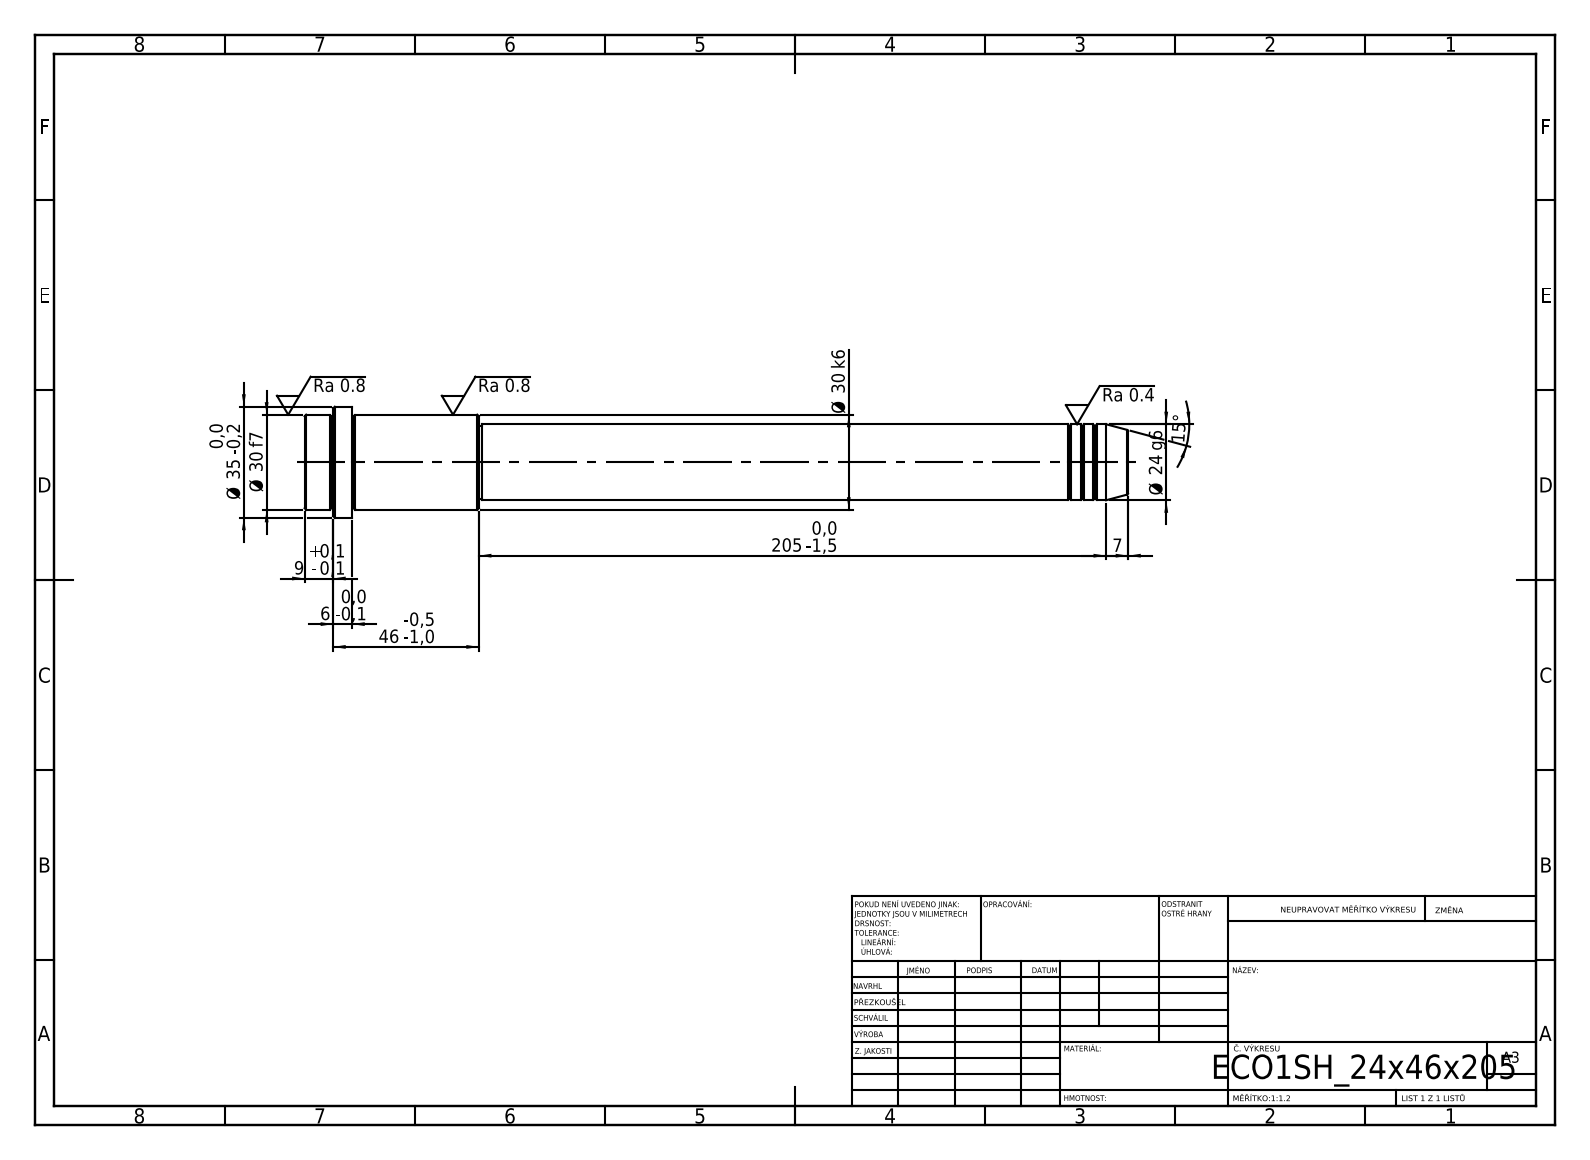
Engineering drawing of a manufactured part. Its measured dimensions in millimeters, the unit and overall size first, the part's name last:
Units: millimetres
Overall size (bounding box): 260 × 35 × 35
Round bosses / shafts (diameter × count): ⌀35 ×1, ⌀30 ×1, ⌀24 ×1, ⌀23 ×1
Main face-to-face distances: 260, 245, 15, 205, 40, 55, 251, 46, 6, 9
Volume: 132 444 mm³ · Surface area: 22 700 mm²
Bodies: 1 solid, 52 faces (6 planar, 16 cylindrical, 30 other)
STEP written by: SolidWorks 2019 (CONFIG_CONTROL_DESIGN)
